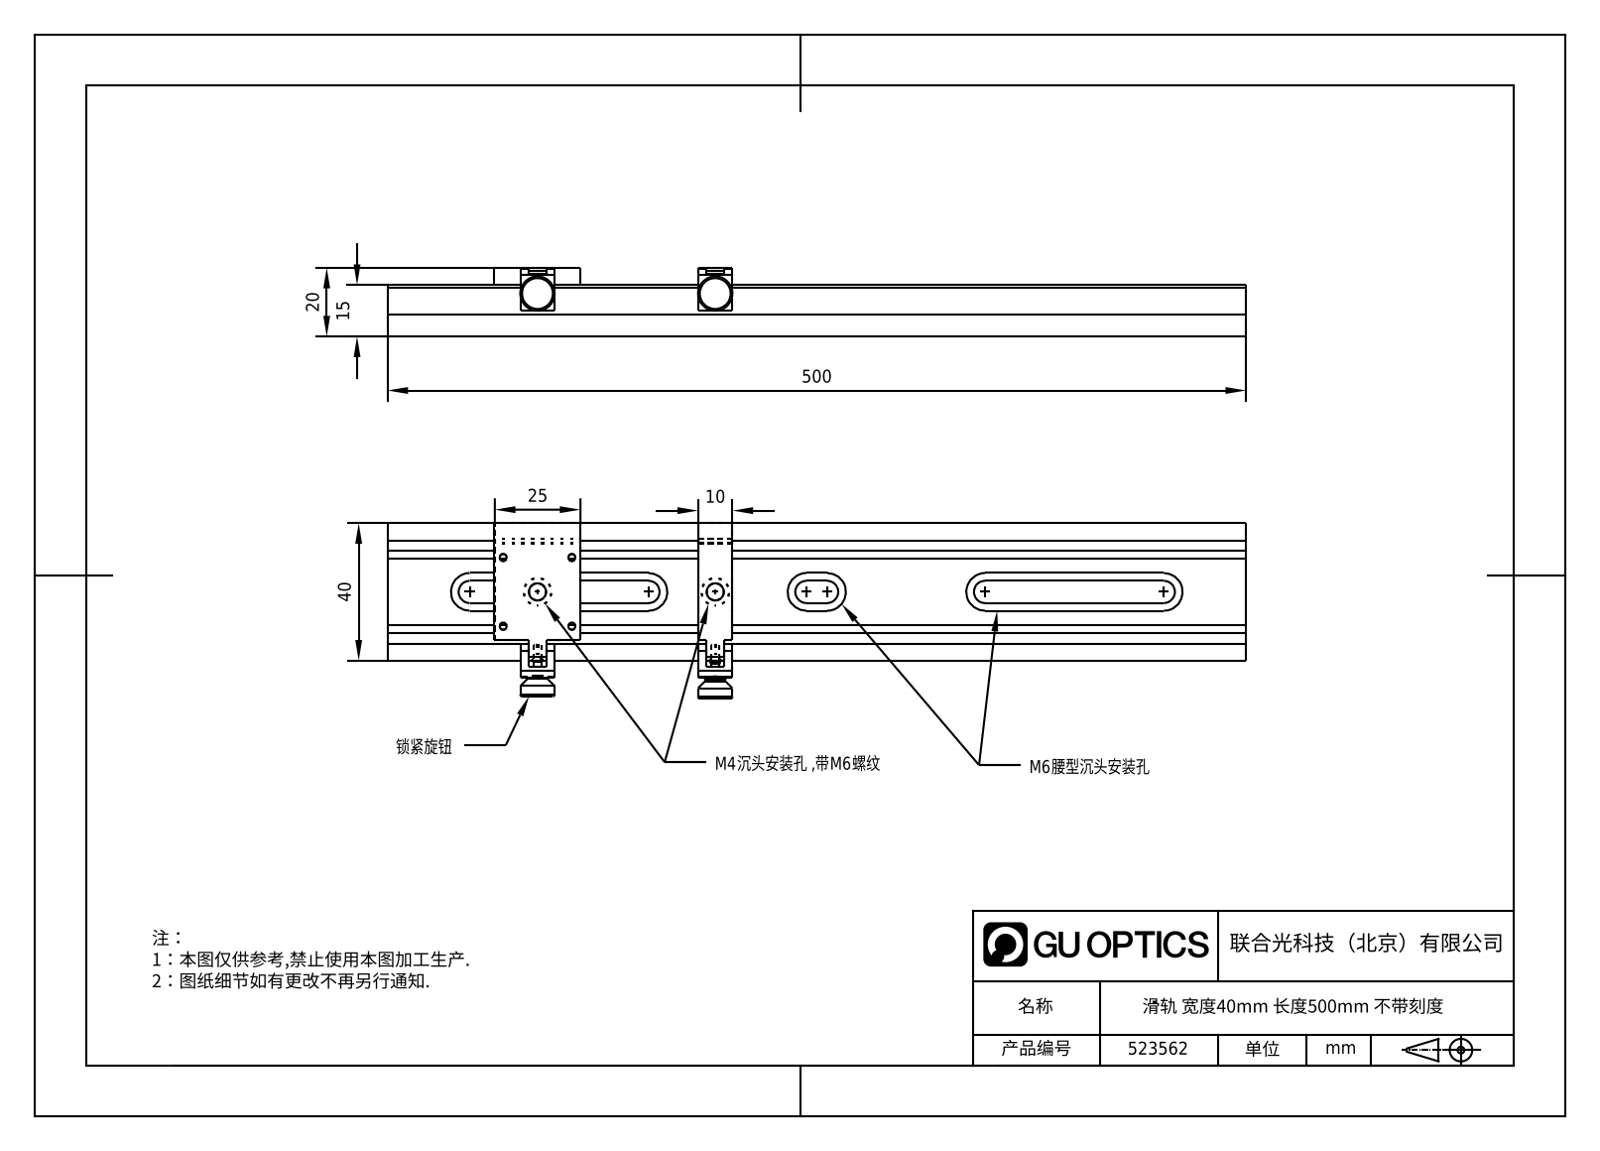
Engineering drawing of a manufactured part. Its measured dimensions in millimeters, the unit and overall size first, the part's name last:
Units: millimetres
Overall size (bounding box): 500 × 51.03 × 20
Round holes (diameter × count): ⌀2.05 ×4, ⌀2.5 ×2, ⌀3.2 ×2, ⌀5 ×2, ⌀8 ×2, ⌀1.5 ×1, ⌀2 ×1
Round bosses / shafts (diameter × count): ⌀10 ×2, ⌀6 ×2, ⌀3 ×2, ⌀2.2 ×2
Partial cylindrical surfaces — rounded edges, fillets, slot ends (radius × count): R3.25 ×14, R5.5 ×14, R1.25 ×1, R2.5 ×1, R4.5 ×1, R12.5 ×1
Main face-to-face distances: 6, 14.5, 0.5, 6.5, 15, 5, 8.5, 40, 8, 9.5
Hole centre spacings: 14.14, 20, 28.28, 67.37, 76.62, 87.2
Volume: 185 782 mm³ · Surface area: 73 391 mm²
Bodies: 8 solids, 257 faces (130 planar, 99 cylindrical, 28 other)
Part name (STEP PRODUCT): 4.2.1.5_H40G-500_40mm滑轨，长度500mm，附带两个H40Z滑轨安装座
STEP written by: SolidWorks 2021 (CONFIG_CONTROL_DESIGN)
